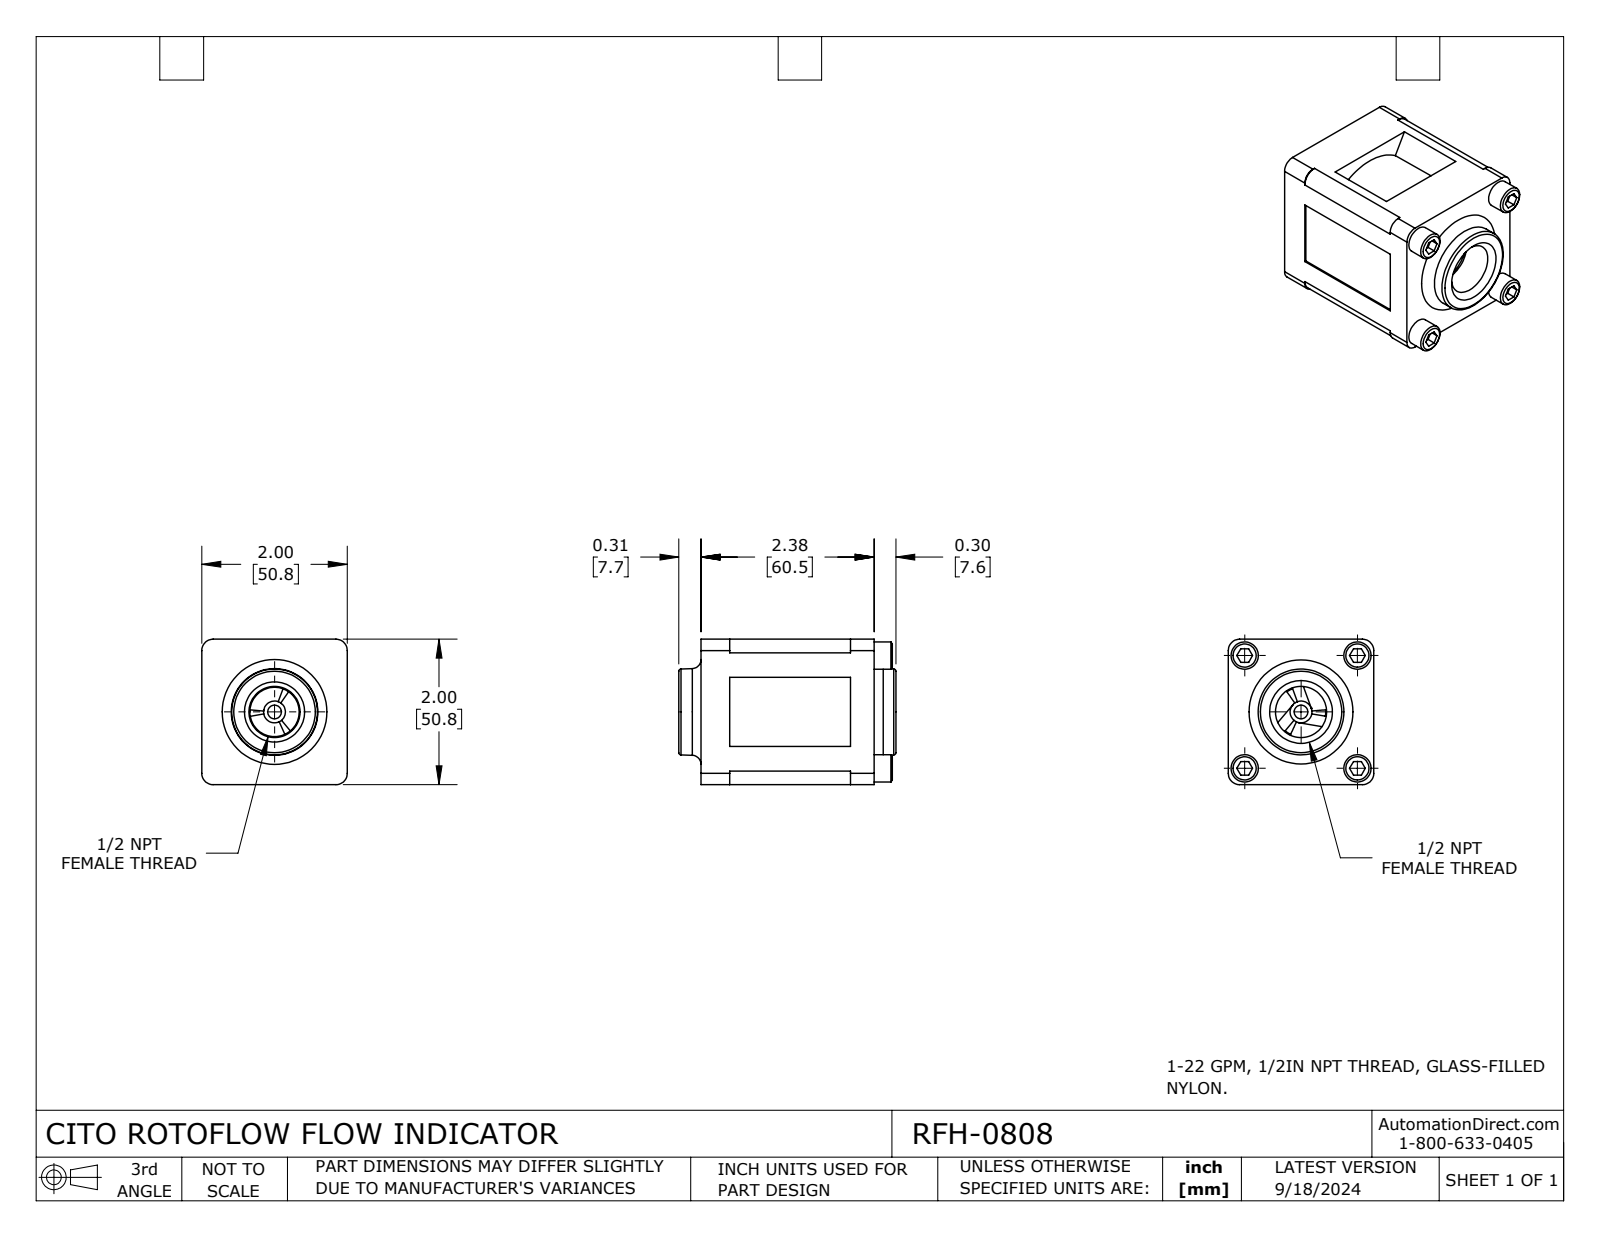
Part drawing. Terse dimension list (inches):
name: RFH-0808
written by: SolidWorks 2023 (CONFIG_CONTROL_DESIGN)
unit: in
bodies: 3 solids, 223 faces (102 planar, 72 cylindrical, 49 other)
size: 2.985 × 2 × 2
volume: 6.012 in³; area: 69.66 in²
holes: 4× ⌀0.201, 4× ⌀0.257, 1× ⌀0.187, 1× ⌀0.3, 1× ⌀0.703, 1× ⌀1.45
bosses: 4× ⌀0.375, 1× ⌀1.179
rounds: 4× R0.156, 4× R0.187, 3× R0.046
face distances: 2, 1.98, 0.02, 0.395, 1.985, 2.38, 1.96, 1.59, 0.169, 0.475
hole spacings: 1.096, 1.55, 2.191
